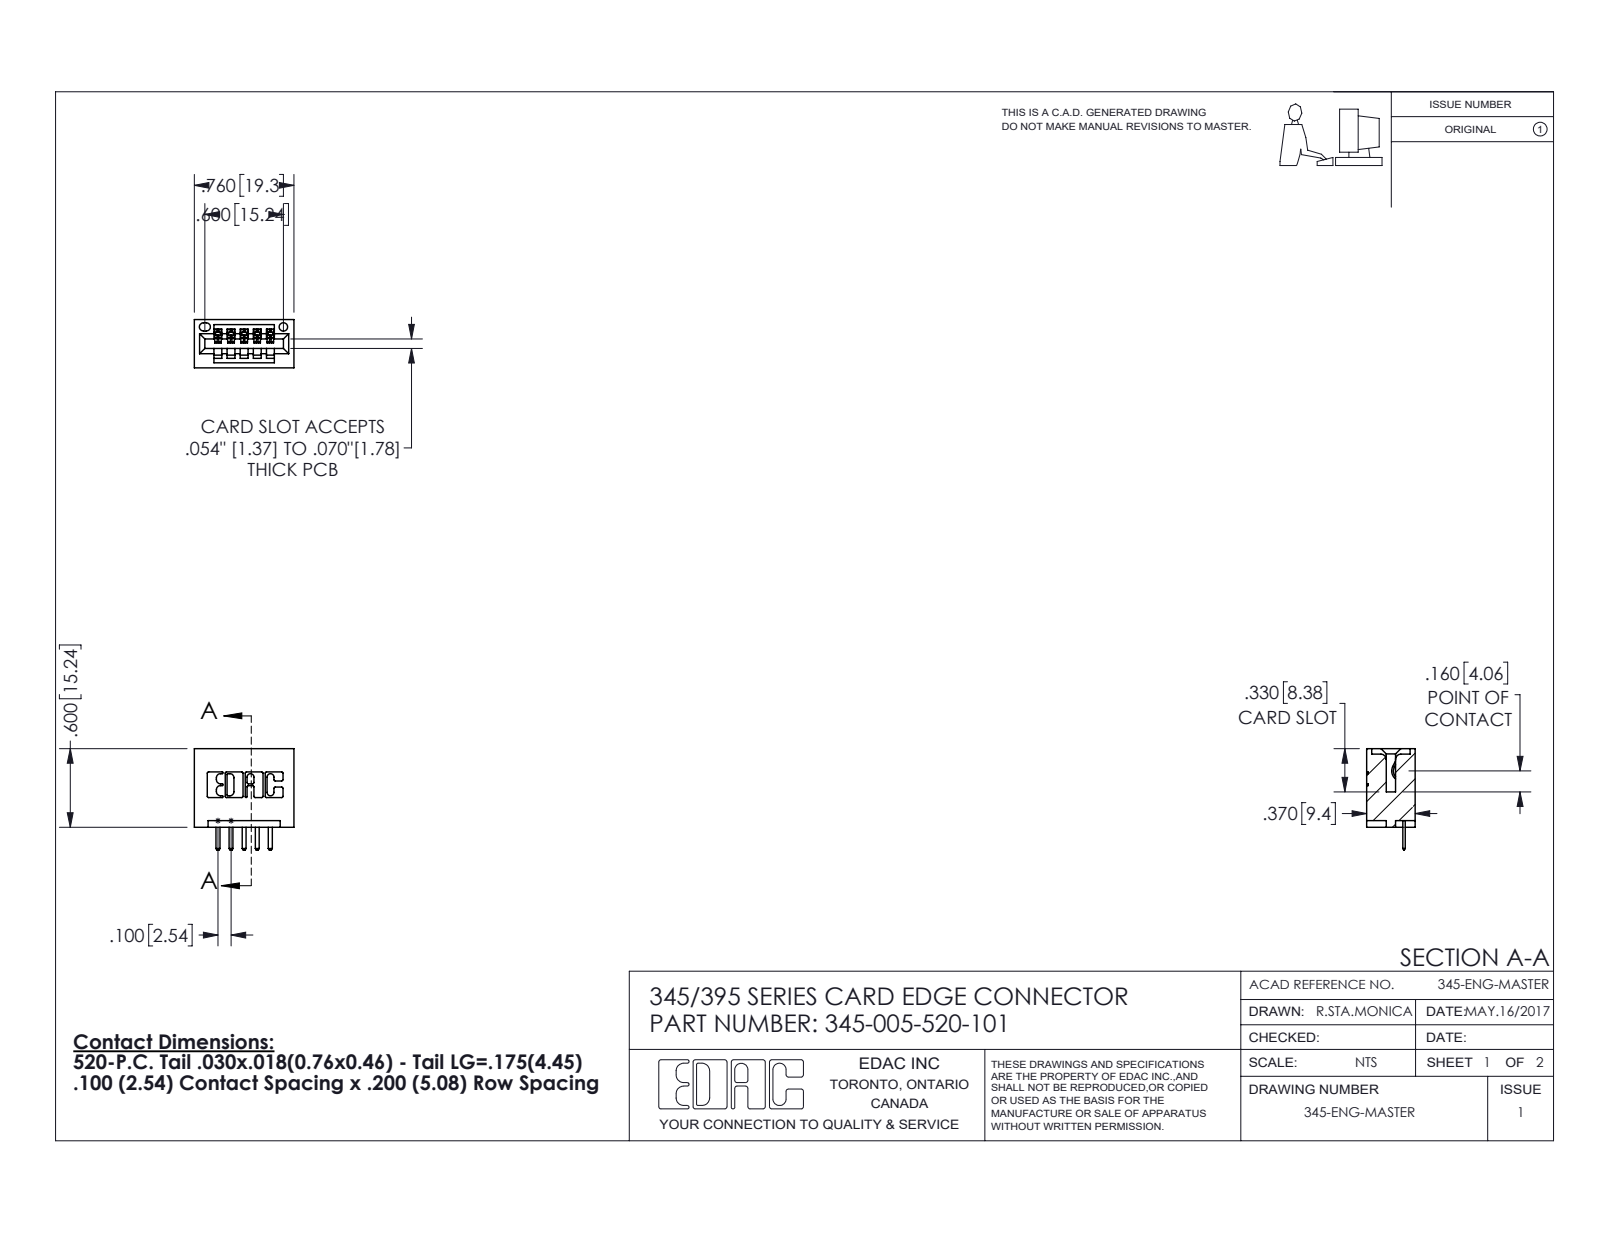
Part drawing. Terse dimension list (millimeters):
name: 345-292-001_345-293-120; 345-005-520-101; 345 Part_No Mounting Lugs
written by: SolidWorks 2016 (CONFIG_CONTROL_DESIGN)
unit: mm
bodies: 6 solids, 428 faces (286 planar, 142 cylindrical, 0 other)
size: 19.7 × 19.3 × 9.4
volume: 2 100 mm³; area: 2 432 mm²
holes: 1× ⌀1.6
rounds: 22× R0.3, 12× R0.3, 10× R0.2, 6× R0.2, 6× R0.8, 3× R0.7, 2× R0.8, 2× R1
face distances: 5.1, 2.5, 9.4, 7.6, 1.8, 1.5, 0.6, 19.3, 14, 2.5
